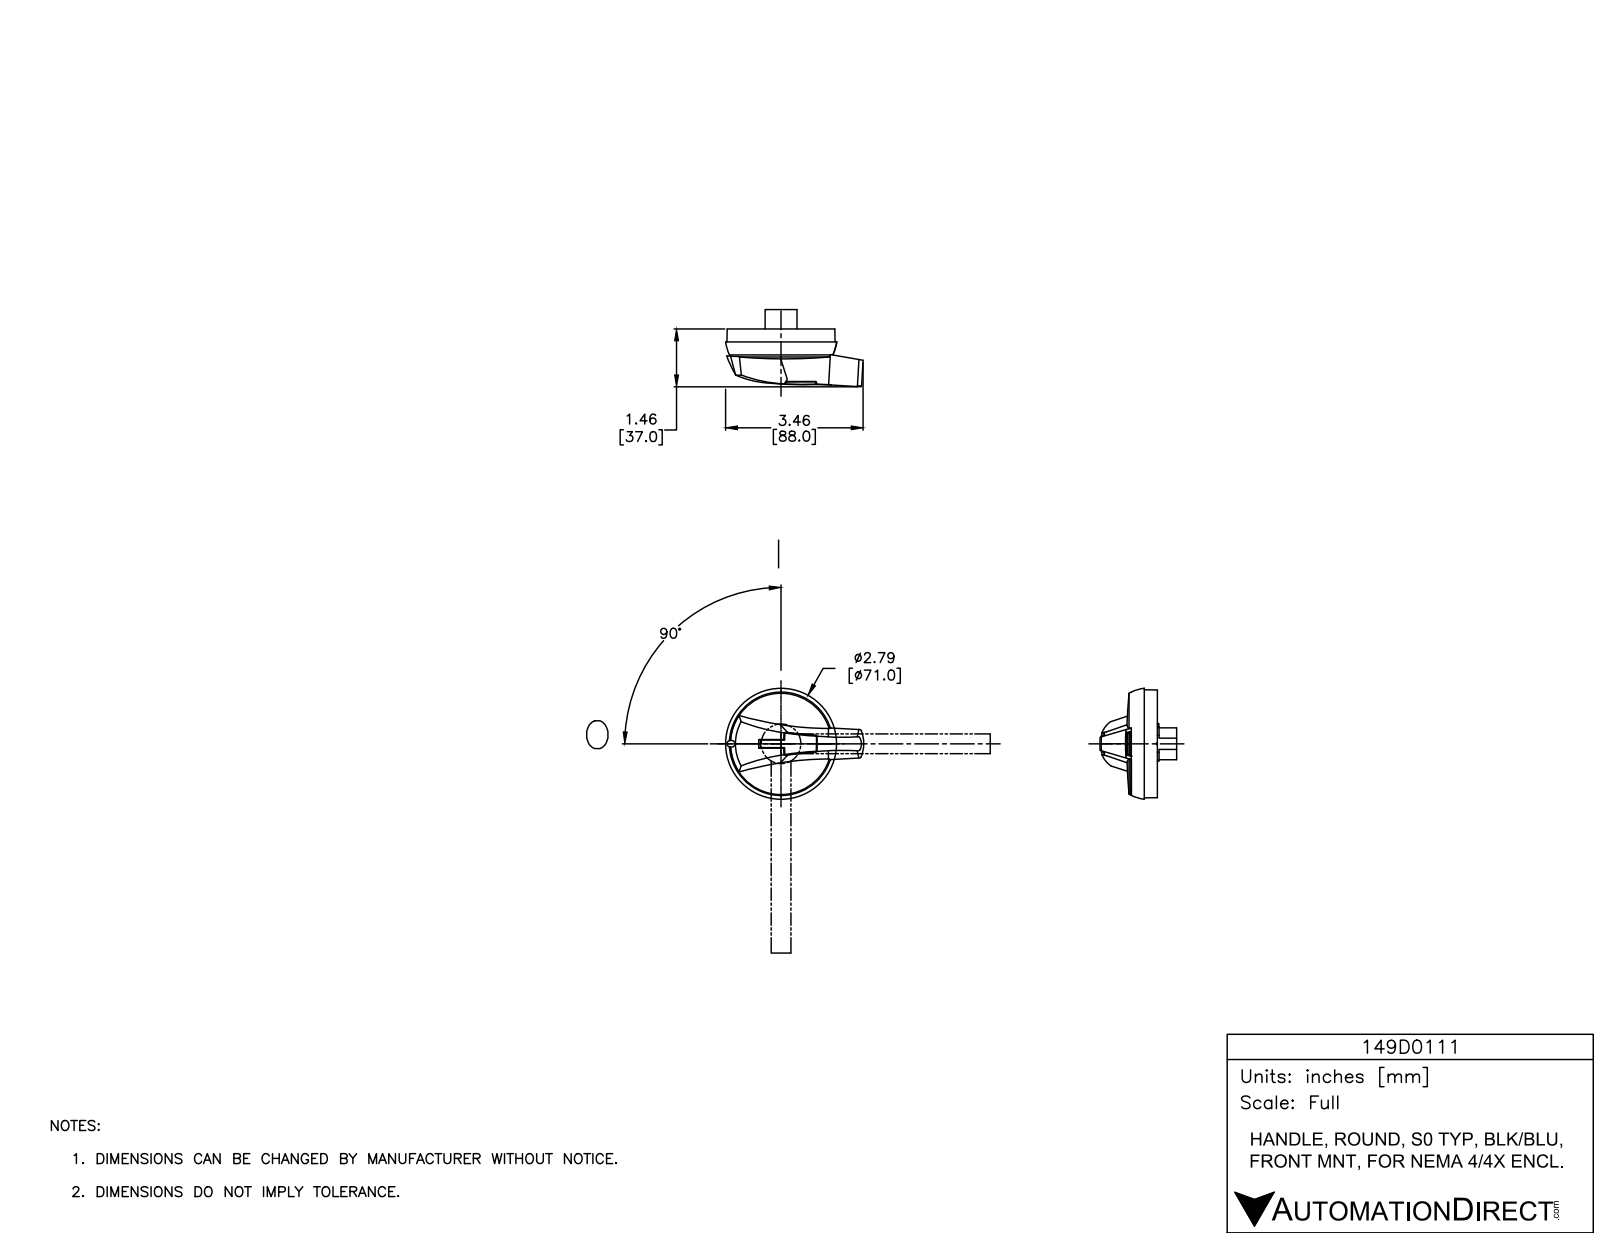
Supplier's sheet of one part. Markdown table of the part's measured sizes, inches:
| quantity | value |
| --- | --- |
| part name | 149D0111 |
| STEP written by | SolidWorks 2015 (AUTOMOTIVE_DESIGN) |
| units | inches |
| bodies | 6 solids, 2118 faces (468 planar, 373 cylindrical, 1277 other) |
| overall size | 3.479 × 2.8 × 1.925 |
| volume | 3.457 in³ |
| surface area | 93.25 in² |
| round holes (diameter × count) | 0.169 × 4, 0.193 × 4, 0.394 × 4, 0.079 × 3, 0.13 × 2, 0.157 × 2, 0.335 × 2, 0.118 × 1, 0.126 × 1, 0.457 × 1, 0.89 × 1, 2.618 × 1 |
| round bosses / shafts (diameter × count) | 2.559 × 1, 0.984 × 1 |
| partial cylindrical surfaces (radius × count) | 0.02 × 114, 0.039 × 23, 0.01 × 19, 0.012 × 10, 0.03 × 8, 0.641 × 6, 0.142 × 4, 0.187 × 4 |
| main face-to-face distances | 0.059, 0.071, 0.13, 0.616, 0.053, 0.03, 0.557, 0.486, 0.152, 0.295 |
| hole center spacings | 0.564, 0.961, 1.557, 0.669, 0.677, 1.102, 1.181, 1.575 |
